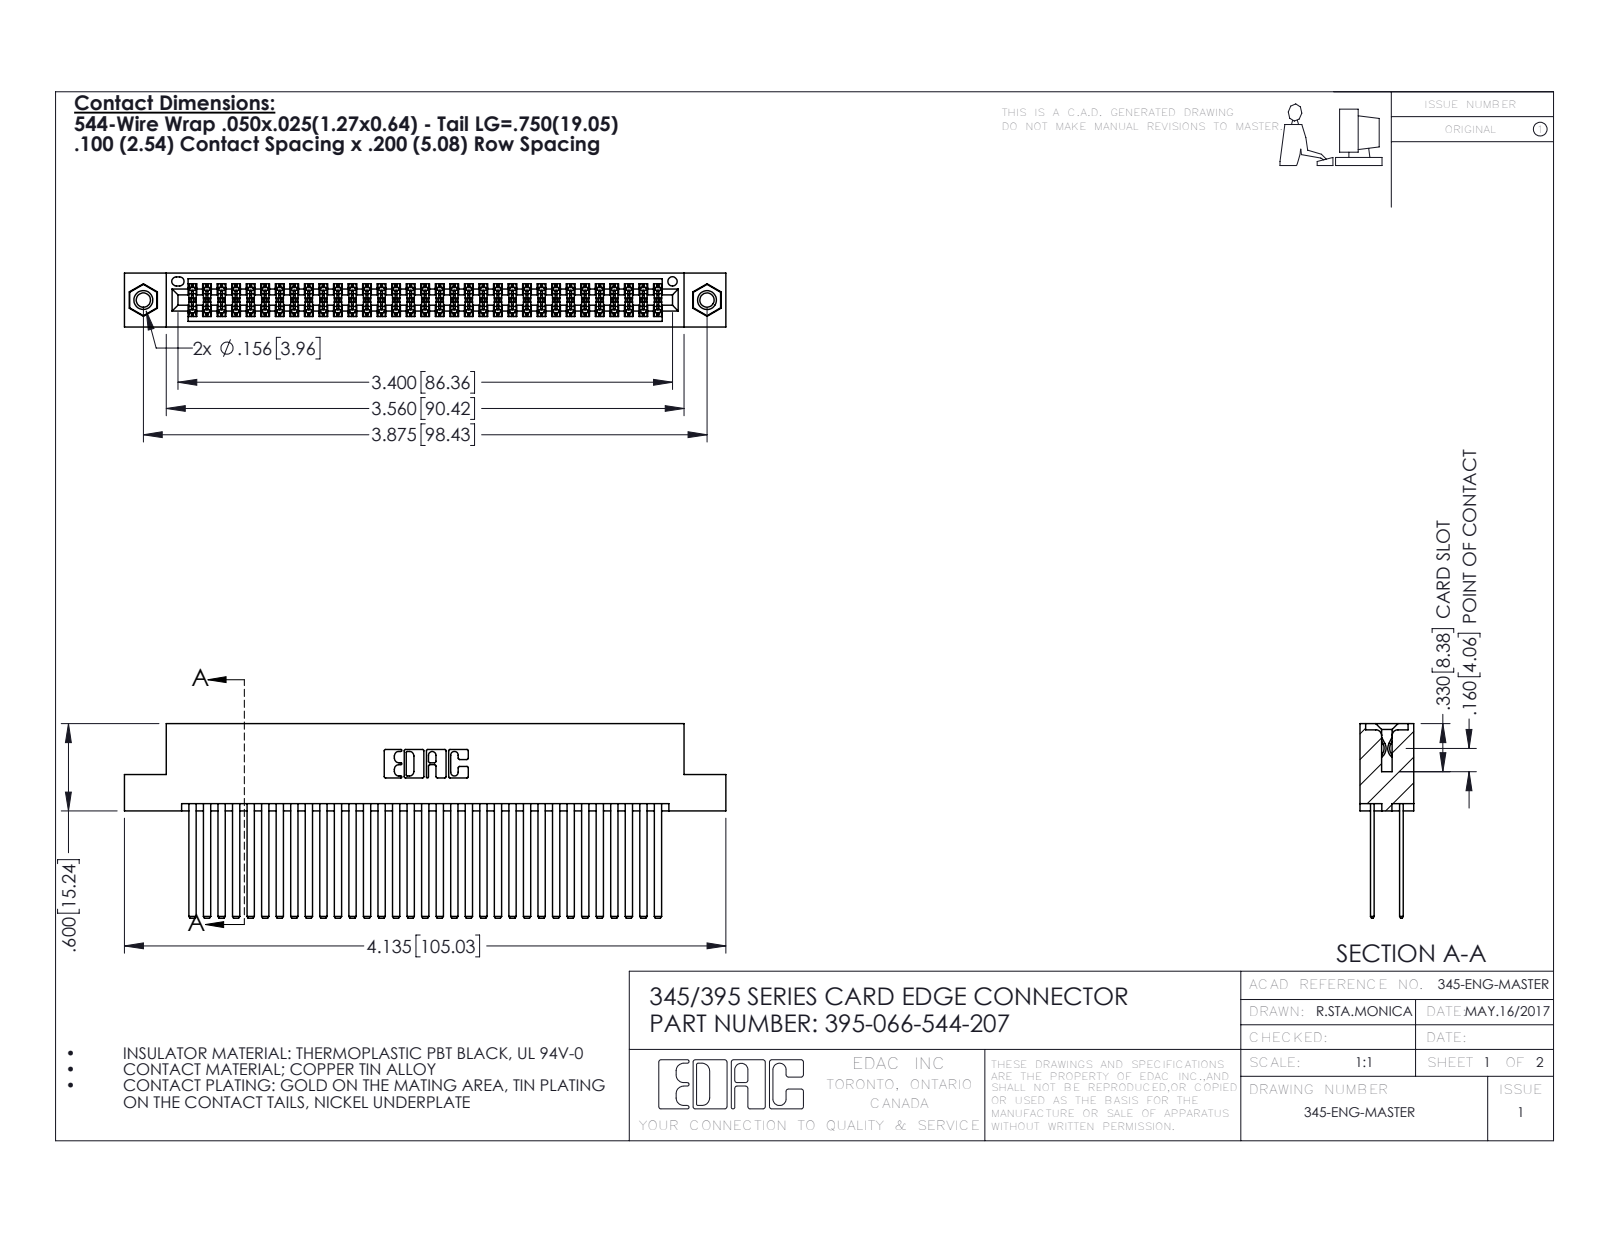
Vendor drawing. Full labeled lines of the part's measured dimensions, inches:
Part name (STEP PRODUCT): 345-292-001_345-293-144; 395-066-544-207; 345-250-001_345-250-005-103; 345 Part_Flush Mounting Lugs - 0.156 Dia-TI
STEP written by: SolidWorks 2016 (CONFIG_CONTROL_DESIGN)
Units: inches
Bodies: 69 solids, 3090 faces (2026 planar, 1048 cylindrical, 16 other)
Overall size (bounding box): 4.135 × 1.337 × 0.37
Volume: 0.673 in³ · Surface area: 29.25 in²
Round holes (diameter × count): ⌀0.098 ×2, ⌀0.125 ×2, ⌀0.156 ×2, ⌀0.064 ×1
Round bosses / shafts (diameter × count): ⌀0.155 ×2
Partial cylindrical surfaces — rounded edges, fillets, slot ends (radius × count): R0.006 ×99, R0.01 ×22, R0.007 ×6, R0.031 ×6, R0.026 ×3, R0.014 ×2, R0.019 ×2, R0.022 ×2
Main face-to-face distances: 0.2, 0.025, 0.072, 0.098, 0.272, 0.298, 0.225, 0.175, 0.37, 0.05
Hole centre spacings: 0.27, 3.64, 3.875
